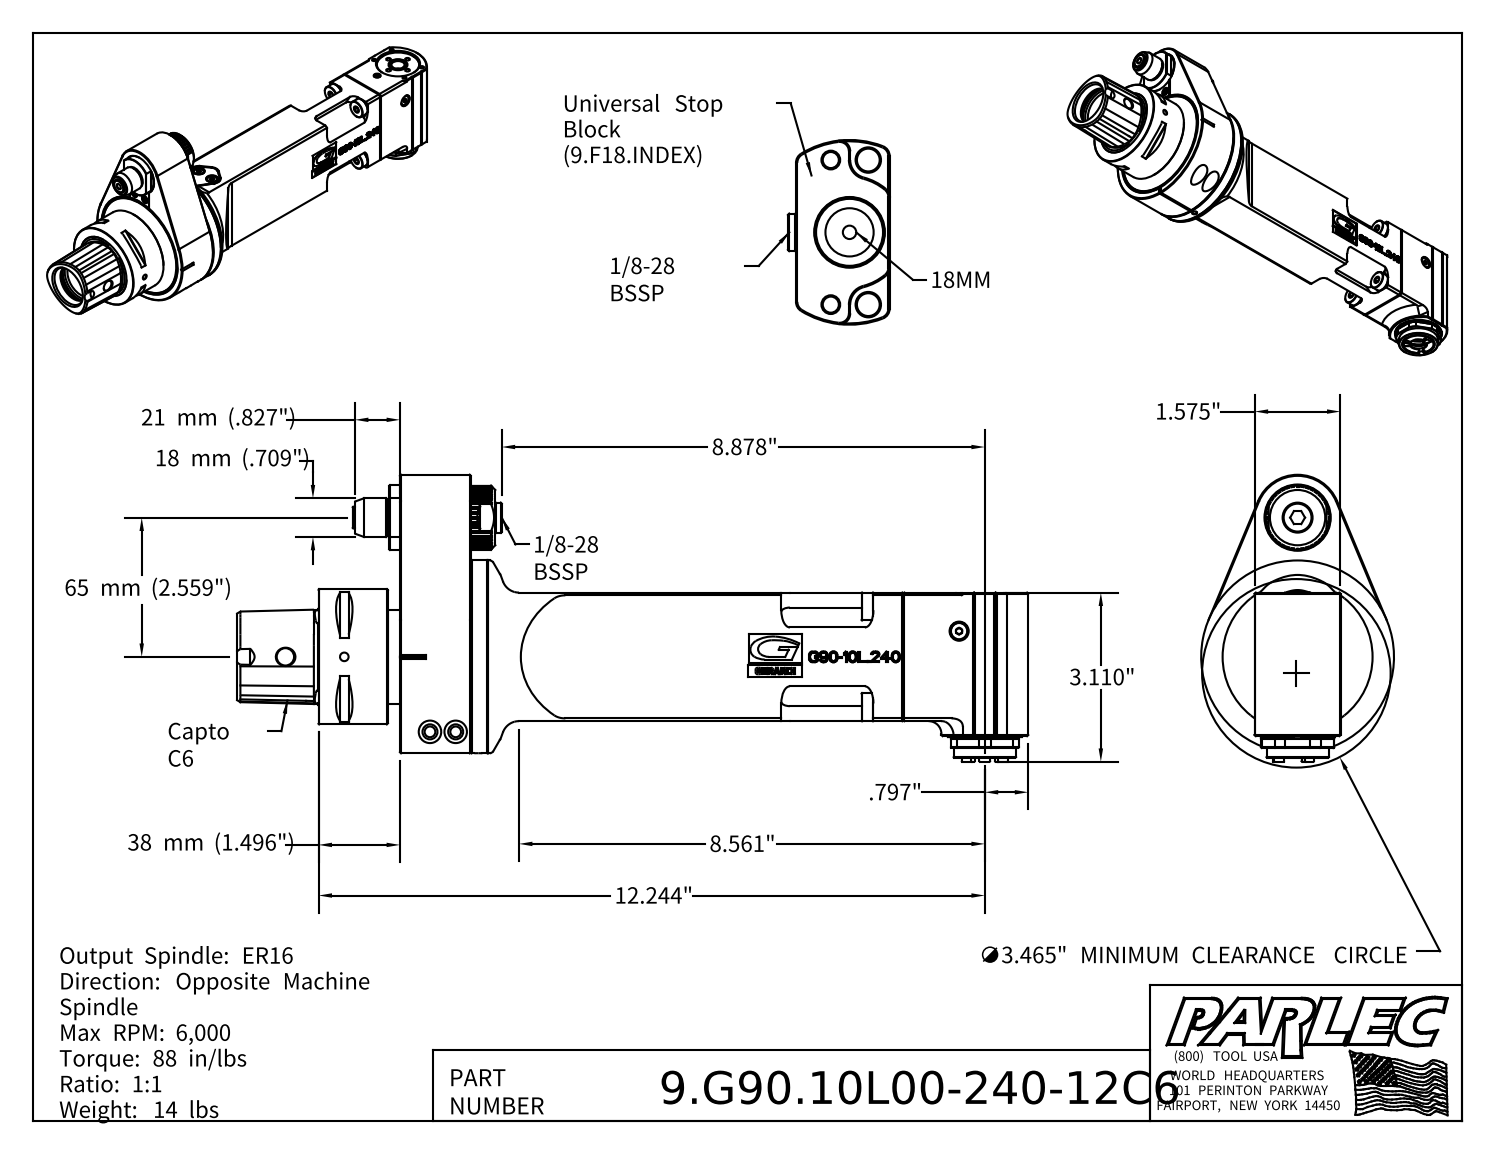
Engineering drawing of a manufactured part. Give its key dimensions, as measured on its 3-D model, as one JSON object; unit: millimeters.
{"part_name": "9.G90.10L00-240-12C6; 9_GA1_666_1 (Type 1, Capto C6, 65mm); 9_G90_10L240", "step_written_by": "Autodesk Inventor 2022 (AUTOMOTIVE_DESIGN)", "units": "millimeters", "bodies": {"solids": 5, "faces": 1561, "planar": 958, "cylindrical": 255, "other": 348}, "overall_size": [369.2, 134, 90], "volume_mm3": 754800, "surface_area_mm2": 199200, "round_holes": [[4.2, 10], [8.5, 5], [2.5, 4], [3, 4], [4, 4], [5, 4], [6, 3], [10.5, 3], [7, 2], [28, 2], [32, 2], [35, 2]], "round_bosses_or_shafts": [[13, 4], [17, 2], [7.8, 2], [90, 1], [82, 1], [78, 1], [70, 1], [63, 1]], "partial_cylinders_radius": [[4, 8], [6, 4], [8, 4], [2, 3], [5, 3], [28.1, 3], [1.5, 2], [2.2, 2]], "face_to_face_distances": [40, 33, 60, 8, 3, 41, 30, 5, 25, 5.7], "hole_center_spacings": [37.5, 18.5, 10, 11, 14.1, 16, 19.4, 25]}
